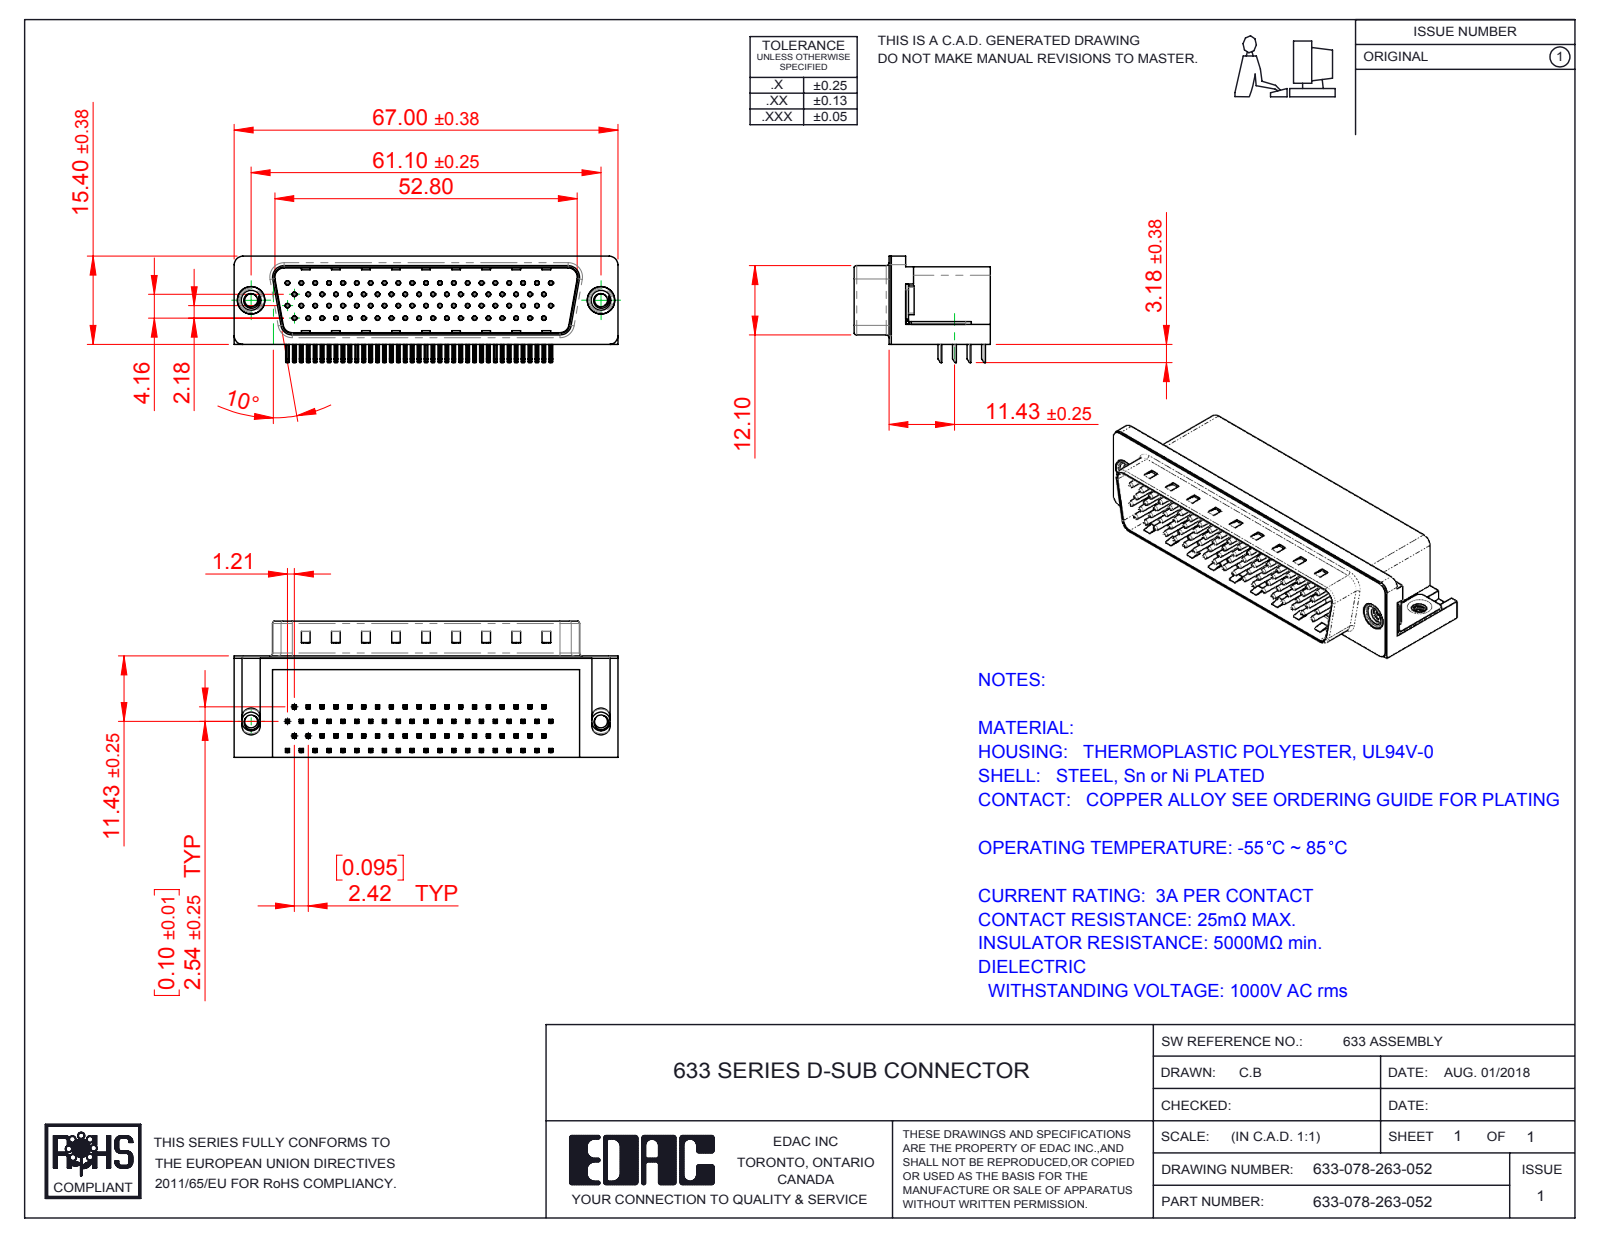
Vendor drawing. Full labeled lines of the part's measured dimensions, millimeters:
Part name (STEP PRODUCT): 633 Housing_78 Contact; 633-078-263-052; 633 Contact Top_78 Contact; 633 Contact Middle_78 Contact (+5 more)
STEP written by: SolidWorks 2016 (CONFIG_CONTROL_DESIGN)
Units: millimetres
Bodies: 84 solids, 6306 faces (3981 planar, 1790 cylindrical, 535 other)
Overall size (bounding box): 67 × 23.8 × 18.58
Volume: 14 625 mm³ · Surface area: 16 428 mm²
Round holes (diameter × count): ⌀0.35 ×78, ⌀0.8 ×78, ⌀2.26 ×4, ⌀4 ×2, ⌀4.8 ×2, ⌀5 ×2
Round bosses / shafts (diameter × count): ⌀0.75 ×78, ⌀4.9 ×2, ⌀4.75 ×2, ⌀3.9 ×2, ⌀3.26 ×2
Partial cylindrical surfaces — rounded edges, fillets, slot ends (radius × count): R0.25 ×320, R0.12 ×156, R1 ×16, R0.5 ×9, R1.6 ×8, R1.5 ×6, R0.45 ×4, R0.9 ×4
Main face-to-face distances: 0.4, 13.2, 17.3, 11.7, 13.35, 2.05, 13.75, 1.65, 1.85, 11.9
Hole centre spacings: 2.42, 4.84, 7.26, 9.68, 6.26, 7.13, 12.1, 8.62
